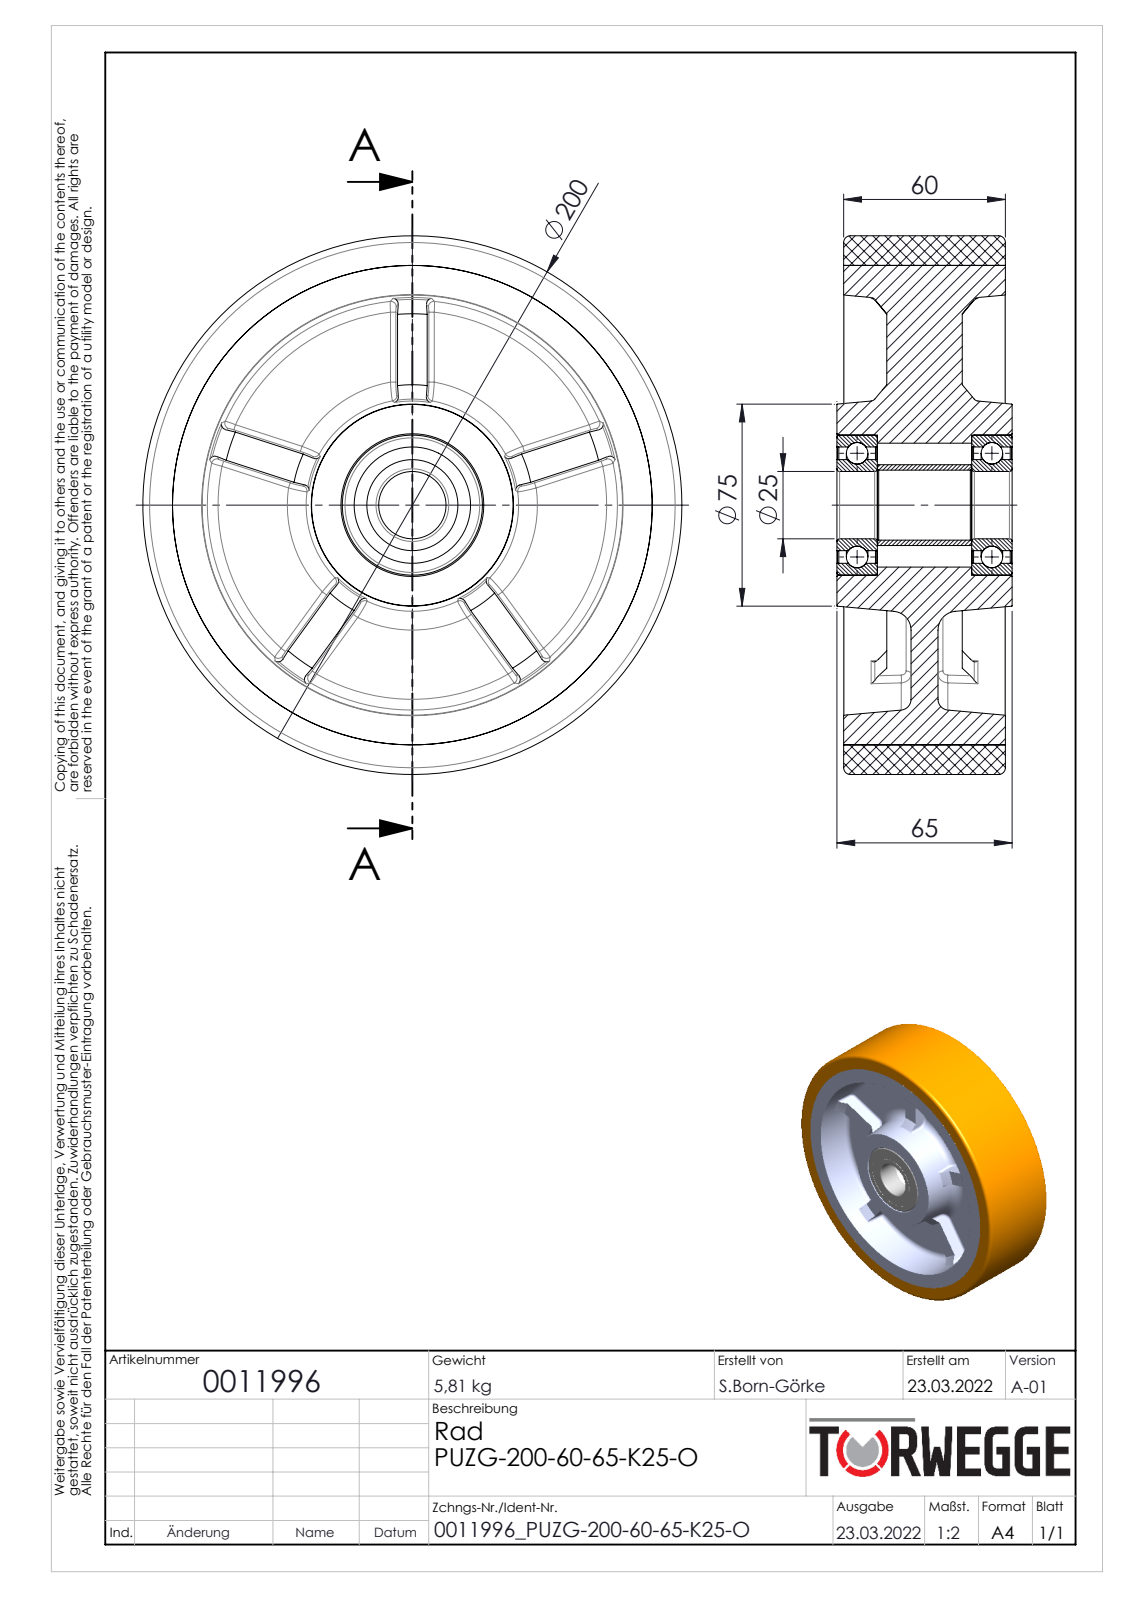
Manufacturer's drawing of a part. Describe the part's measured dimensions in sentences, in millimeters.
The part is named "0011996". Its 3-D file was written by "SolidWorks 2020 (AUTOMOTIVE_DESIGN)". It is 13 solids with 354 faces: 66 planar, 76 cylindrical and 212 other. Overall it measures 200 by 200 by 65 millimeters. Its volume is 1 188 000 cubic millimeters and its surface area 244 347 square millimeters. Round holes: 1 of diameter 25, 1 of diameter 26, 1 of diameter 33.8, 1 of diameter 43.2, 1 of diameter 46, 1 of diameter 52, 1 of diameter 178. Round bosses or shafts: 1 of diameter 200, 1 of diameter 30. Partial cylindrical surfaces (rounded edges, fillets, slot ends): 20 of radius 2. The main face-to-face distances are 35, 25, 60, 10, 2.5, 27.5, 37.5, 62.5, 12.5, 50.
